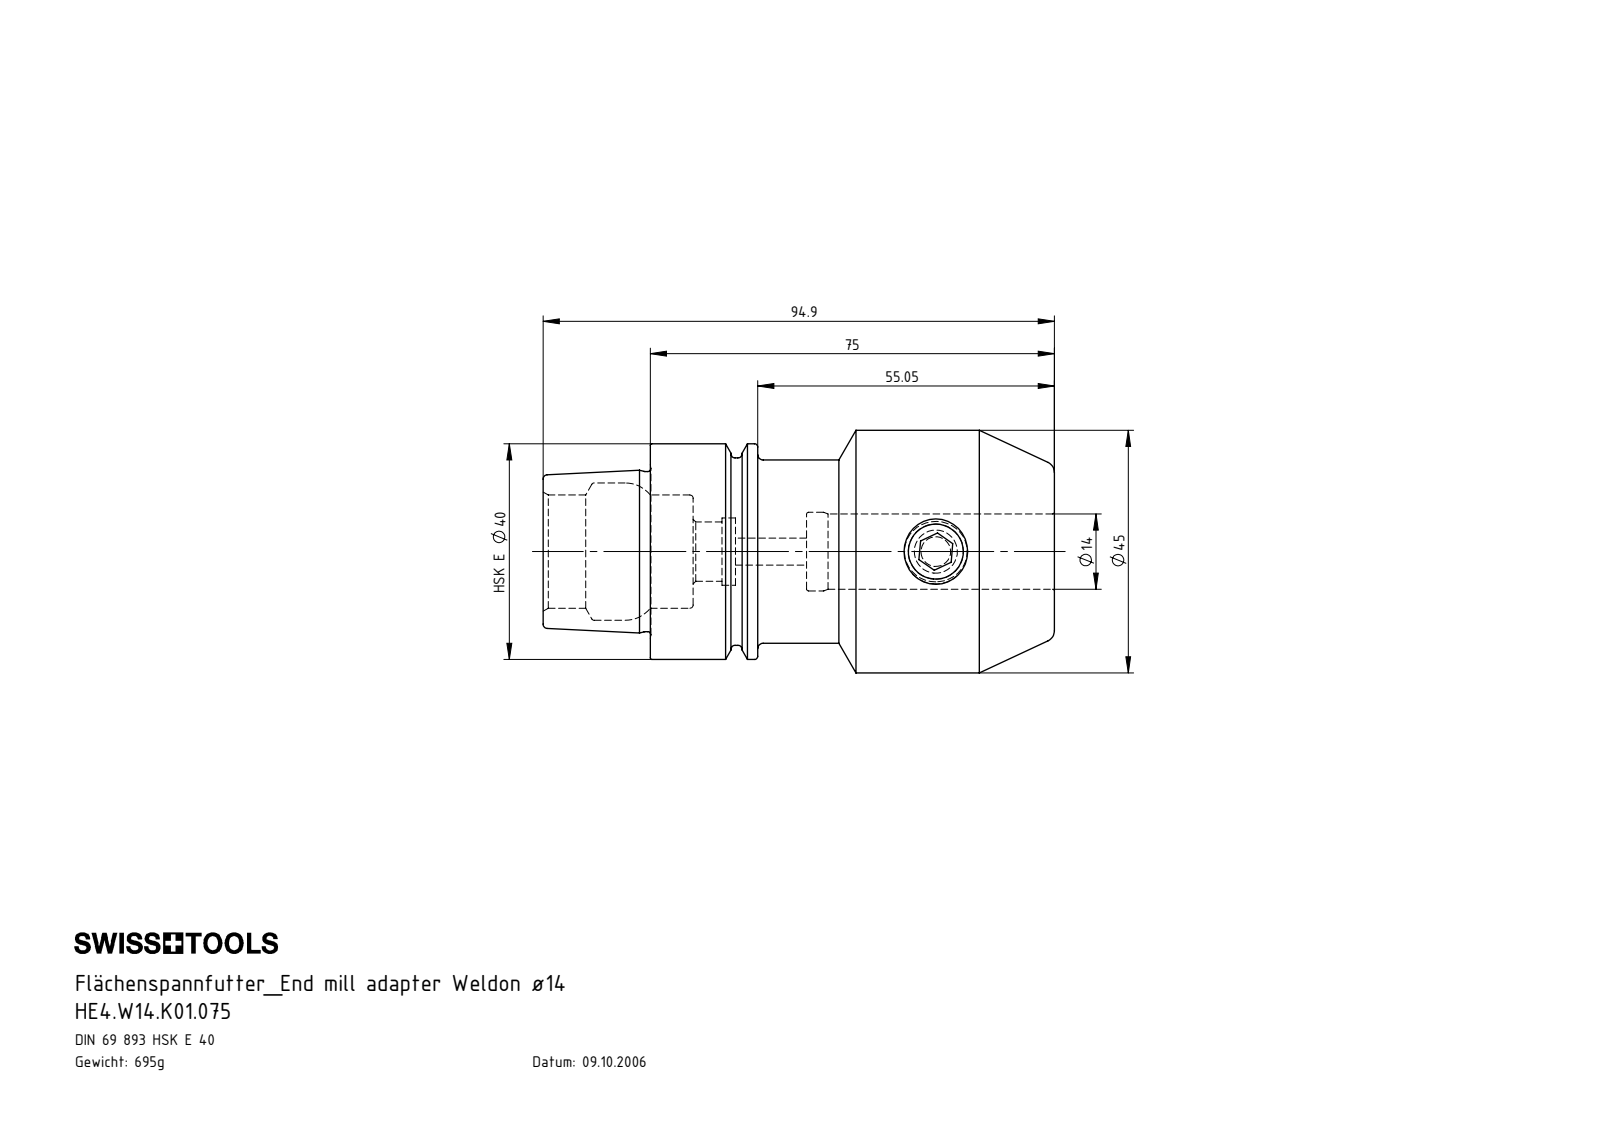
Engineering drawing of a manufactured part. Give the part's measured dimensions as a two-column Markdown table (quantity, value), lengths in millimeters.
| quantity | value |
| --- | --- |
| part name | HE4.W14.K01.075; W12-ER1.001.016; HE4-W14.K01.075_B_Fertigbearbeitung |
| STEP written by | SolidWorks 2012 (AUTOMOTIVE_DESIGN) |
| units | millimeters |
| bodies | 2 solids, 113 faces (19 planar, 32 cylindrical, 62 other) |
| overall size | 94.9 × 45 × 45 |
| volume | 88 503 mm³ |
| surface area | 20 288 mm² |
| round holes (diameter × count) | 5 × 1, 10.25 × 1, 11 × 1, 12.5 × 1, 14 × 1, 14.6 × 1, 21 × 1, 25.5 × 1 |
| round bosses / shafts (diameter × count) | 45 × 1, 40 × 1, 34.75 × 1, 34 × 1, 29.71 × 1, 12 × 1 |
| main face-to-face distances | 75, 7.95, 67.05, 19.9, 27.85, 94.9, 39.85, 19.95, 12, 55.05 |
